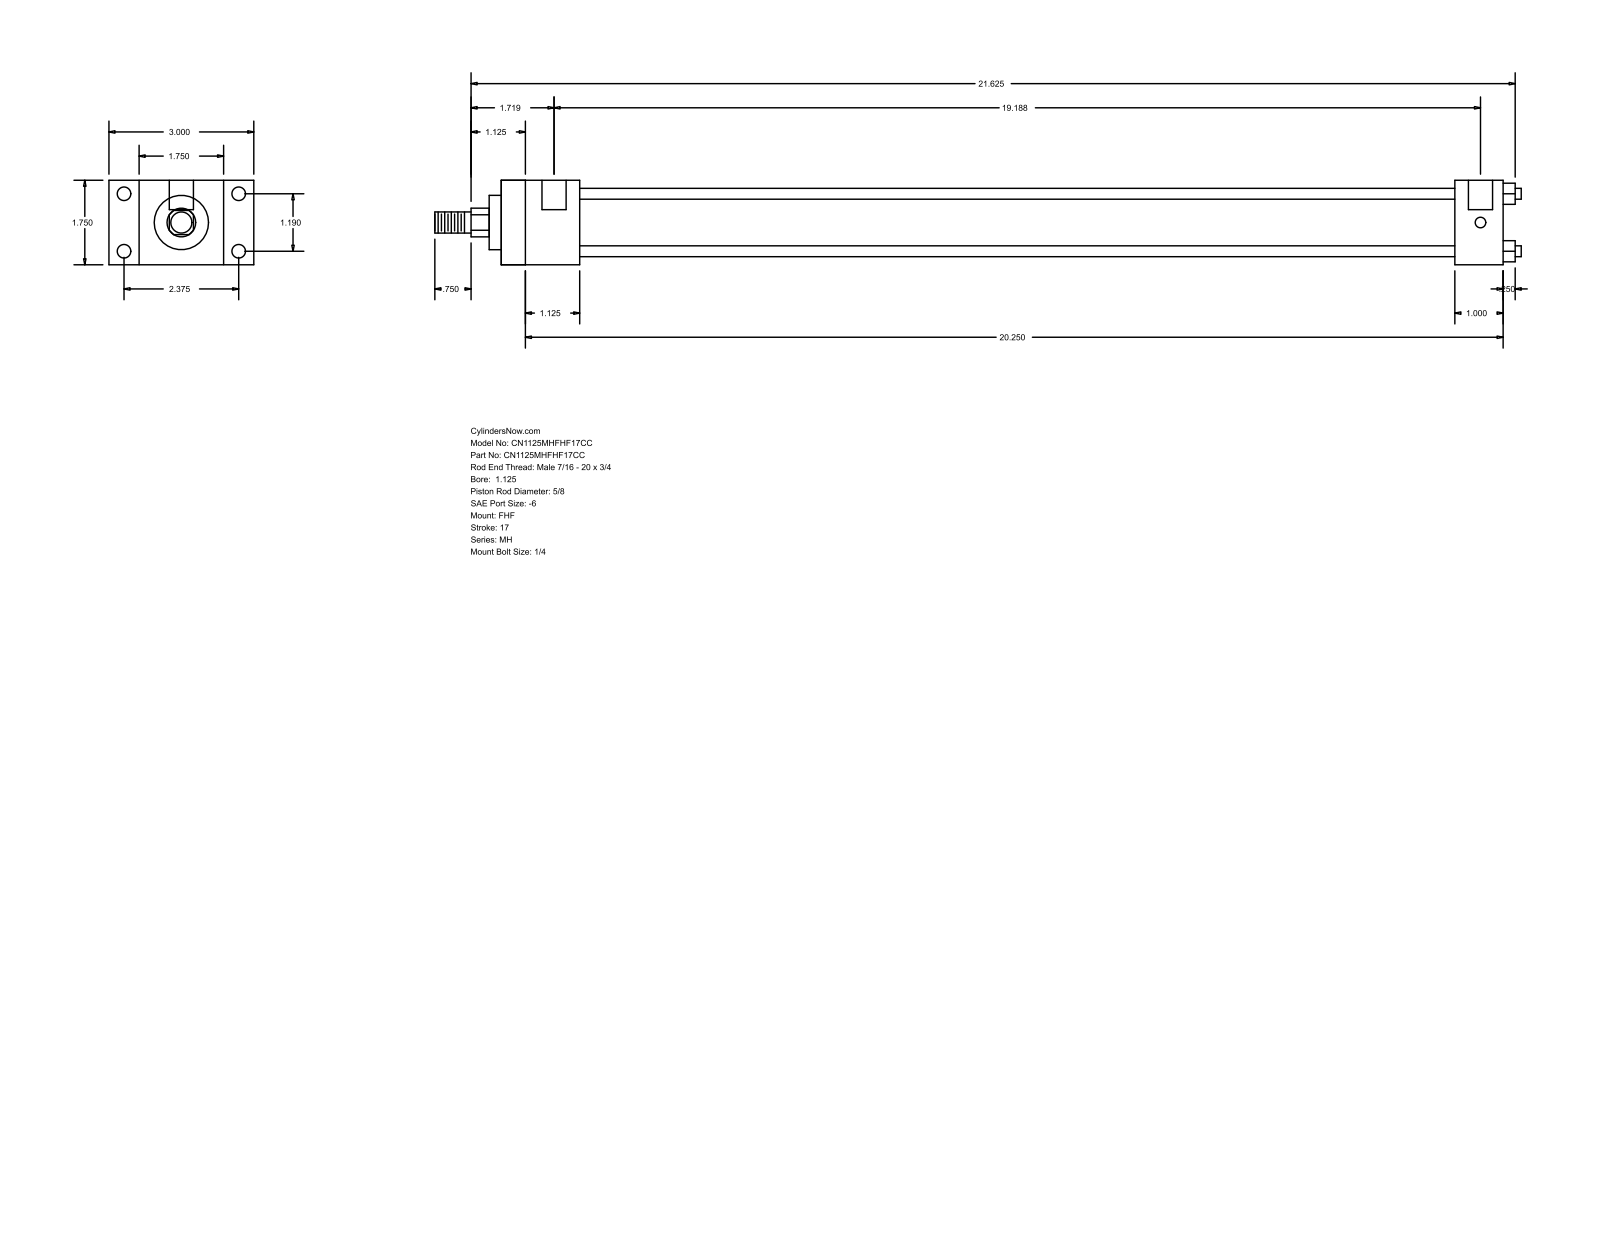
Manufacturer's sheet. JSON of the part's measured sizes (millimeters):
{"part_name": "MH_FHF__0112_0.625", "step_written_by": "GSSL Pune (CONFIG_CONTROL_DESIGN)", "units": "millimeters", "bodies": {"solids": 0, "faces": 88, "planar": 60, "cylindrical": 28, "other": 0}, "overall_size": [571.5, 76.2, 44.45], "round_holes": [[5.56, 4], [7.14, 4], [12.7, 2]], "round_bosses_or_shafts": [[5.71, 4], [34.92, 1], [28.57, 1], [15.88, 1], [11.11, 1]], "partial_cylinders_radius": [[7.54, 1]], "face_to_face_distances": [44.46, 15.87, 60.33, 41.27, 76.2, 527.04, 485.77, 25.4, 501.64, 460.37], "hole_center_spacings": [30.22, 60.32, 67.47, 484.19, 3.17, 487.36]}
